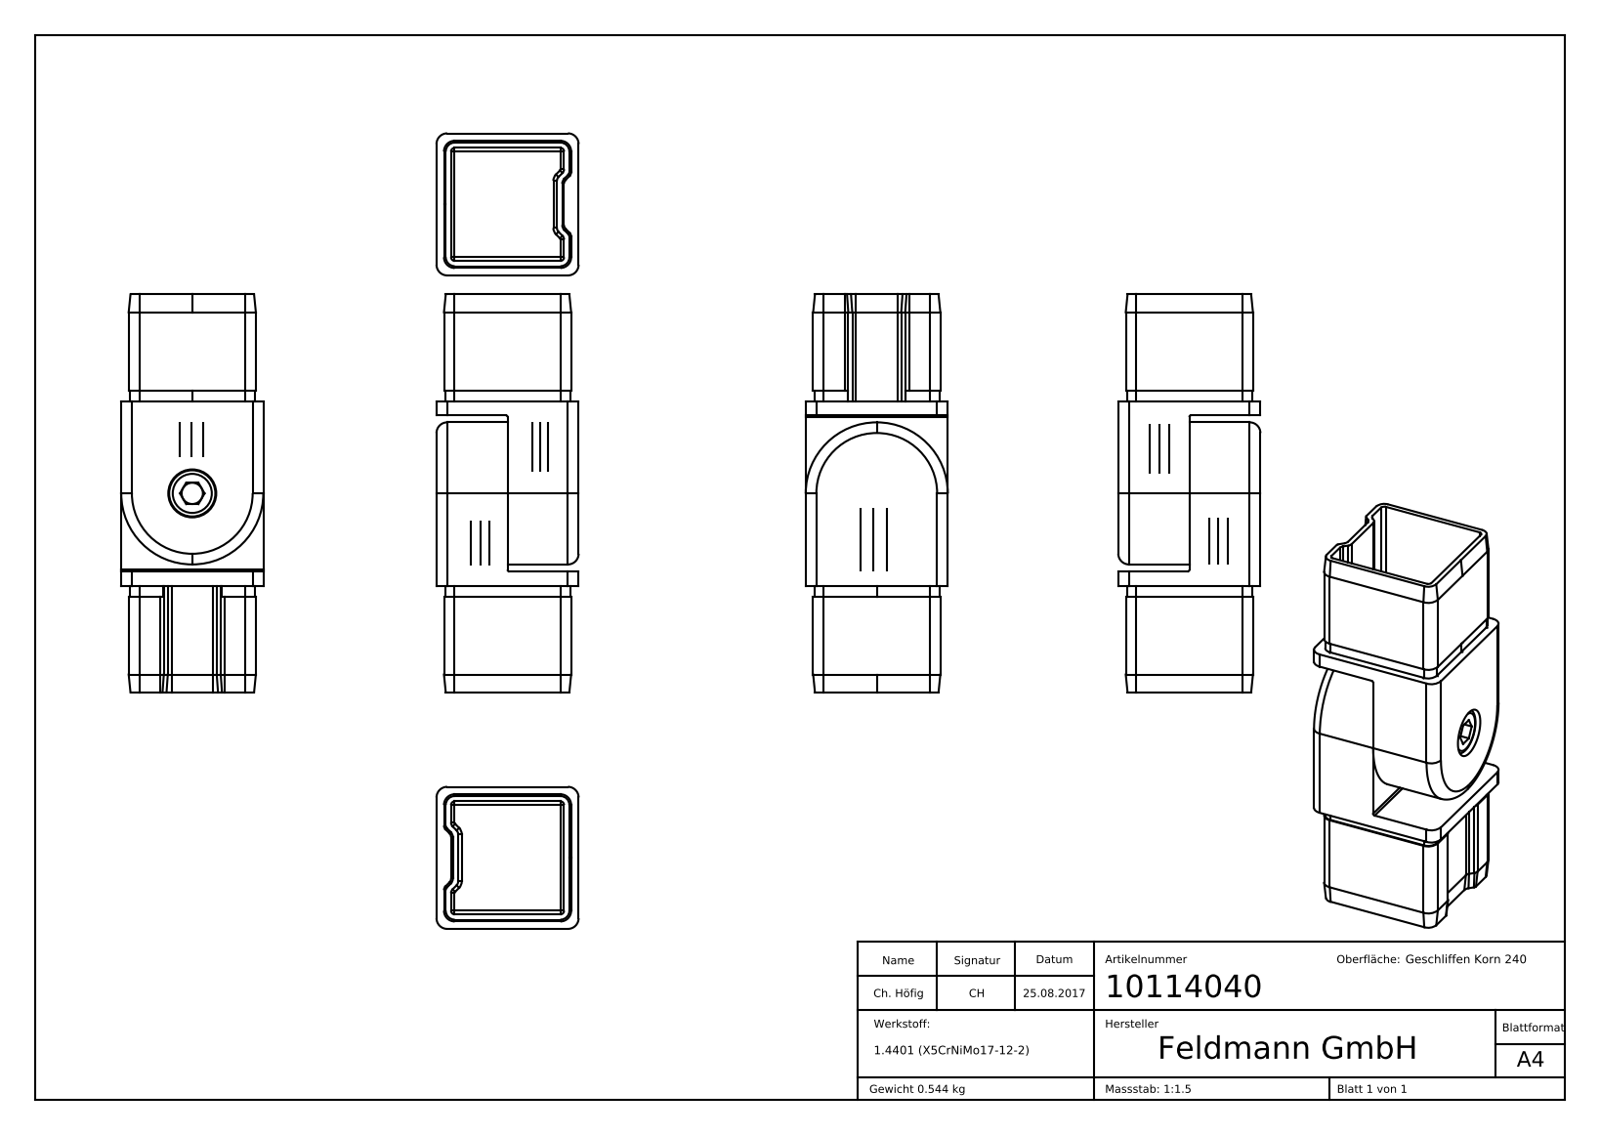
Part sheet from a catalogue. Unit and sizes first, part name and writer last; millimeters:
Units: millimetres
Overall size (bounding box): 112 × 40 × 40
Round holes (diameter × count): ⌀6.8 ×1, ⌀8.5 ×1, ⌀13.5 ×1
Round bosses / shafts (diameter × count): ⌀40 ×1, ⌀13 ×1, ⌀7.19 ×1
Partial cylindrical surfaces — rounded edges, fillets, slot ends (radius × count): R1 ×18, R1.5 ×16, R3 ×8, R2.7 ×4, R0.5 ×2
Main face-to-face distances: 2, 4.1, 35.9, 33.8, 2.1, 31.8, 37.9, 20, 15.9, 40
Volume: 69 561 mm³ · Surface area: 38 198 mm²
Bodies: 3 solids, 445 faces (242 planar, 75 cylindrical, 128 other)
Part name (STEP PRODUCT): 10114040; 1011X0X0 Konfig Teil2_10114040 Teil2; DIN 912 M8x20; 1011X0X0 Konfig Teil1_10114040 Teil1 (+3 more)
STEP written by: SolidWorks 2015 (CONFIG_CONTROL_DESIGN)
